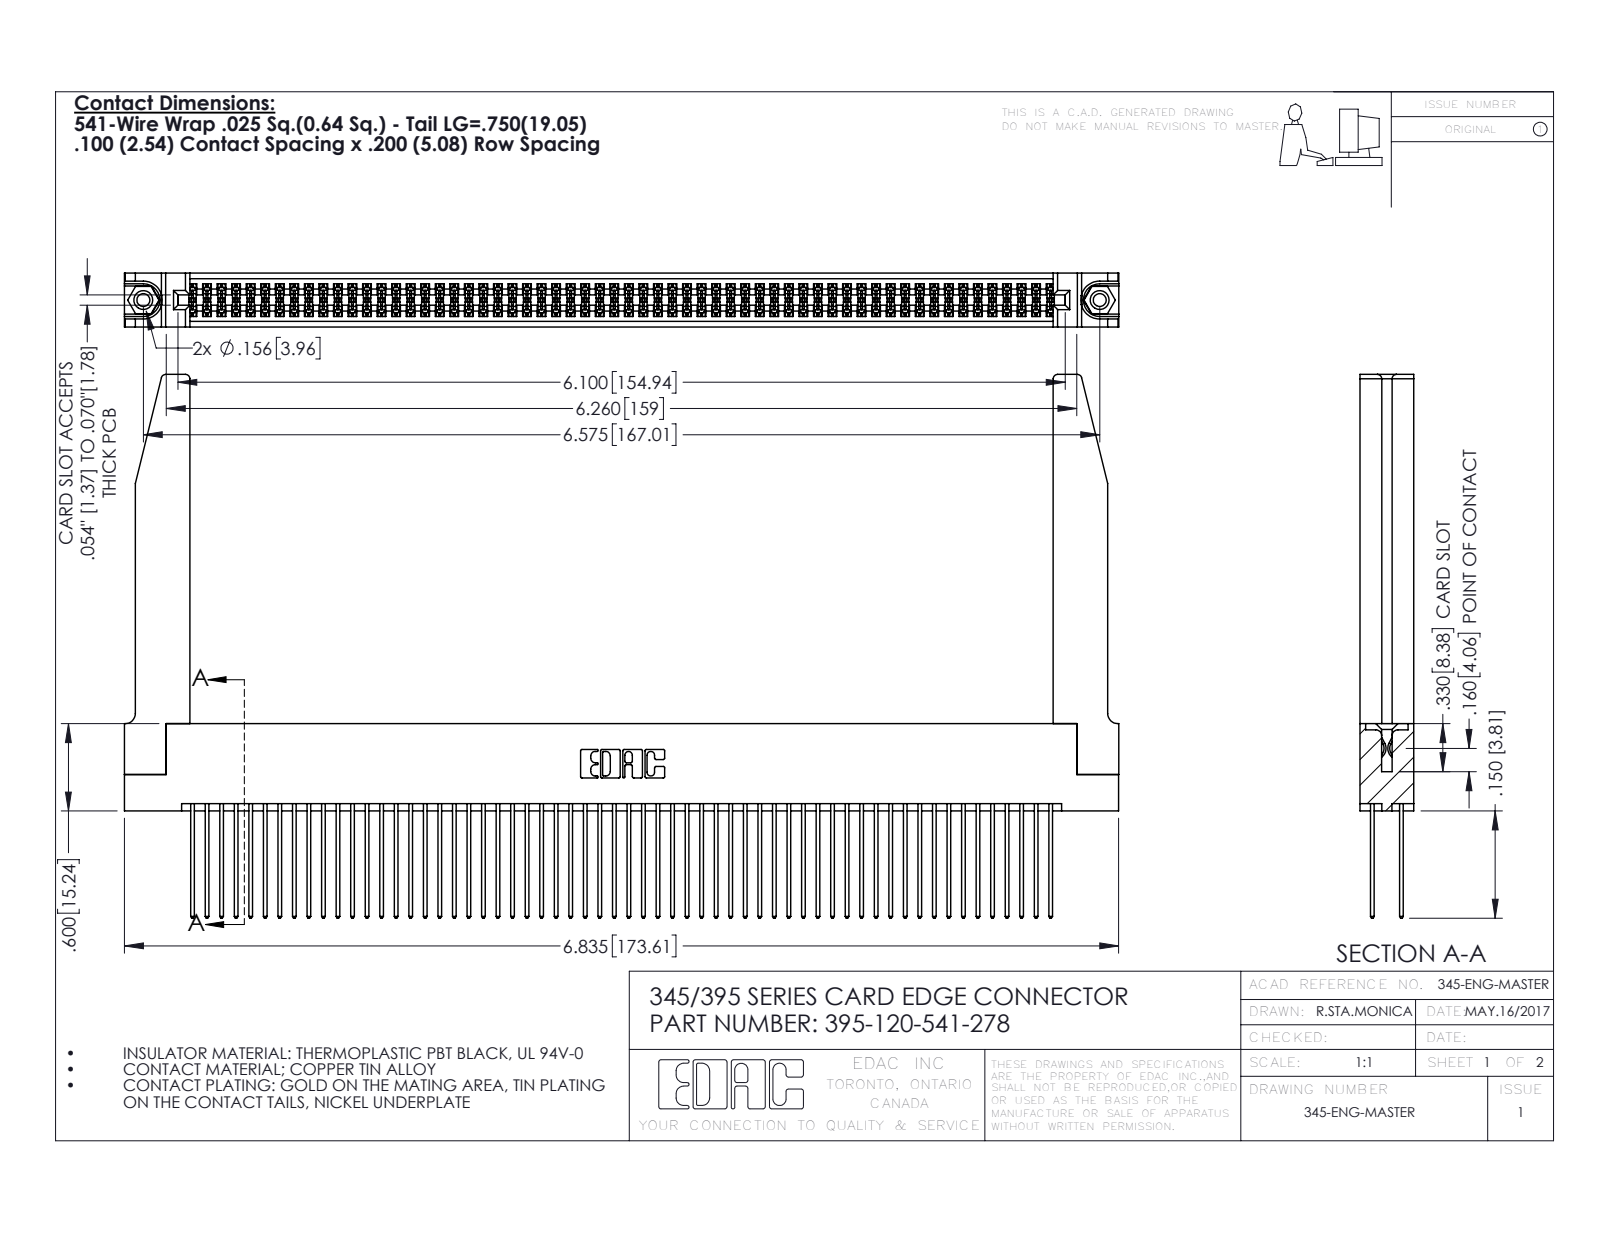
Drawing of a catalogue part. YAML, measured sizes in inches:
part_name: "345 Part_Flush Mounting Lugs - 0.156 Dia-TH; 345-292-001_345-293-141; 345-250-001_345-250-001-102; 345-220-078_345-220-078 (+1 more)"
step_written_by: "SolidWorks 2016 (CONFIG_CONTROL_DESIGN)"
units: inches
bodies: {solids: 125, faces: 6360, planar: 4182, cylindrical: 2126, other: 52}
overall_size: [6.836, 3.737, 0.37]
volume: 1.556
surface_area: 56.76
round_holes:
  - {diameter: 0.089, count: 2}
  - {diameter: 0.125, count: 2}
  - {diameter: 0.156, count: 2}
  - {diameter: 0.064, count: 1}
round_bosses_or_shafts:
  - {diameter: 0.155, count: 2}
partial_cylinders:
  - {radius: 0.006, count: 180}
  - {radius: 0.01, count: 120}
  - {radius: 0.01, count: 22}
  - {radius: 0.03, count: 8}
  - {radius: 0.007, count: 6}
  - {radius: 0.031, count: 6}
  - {radius: 0.026, count: 3}
  - {radius: 0.014, count: 2}
face_to_face_distances: [0.072, 0.298, 0.2, 0.37, 0.098, 0.272, 0.025, 0.225, 0.175, 0.148]
hole_center_spacings: [0.27, 6.339, 6.575]
